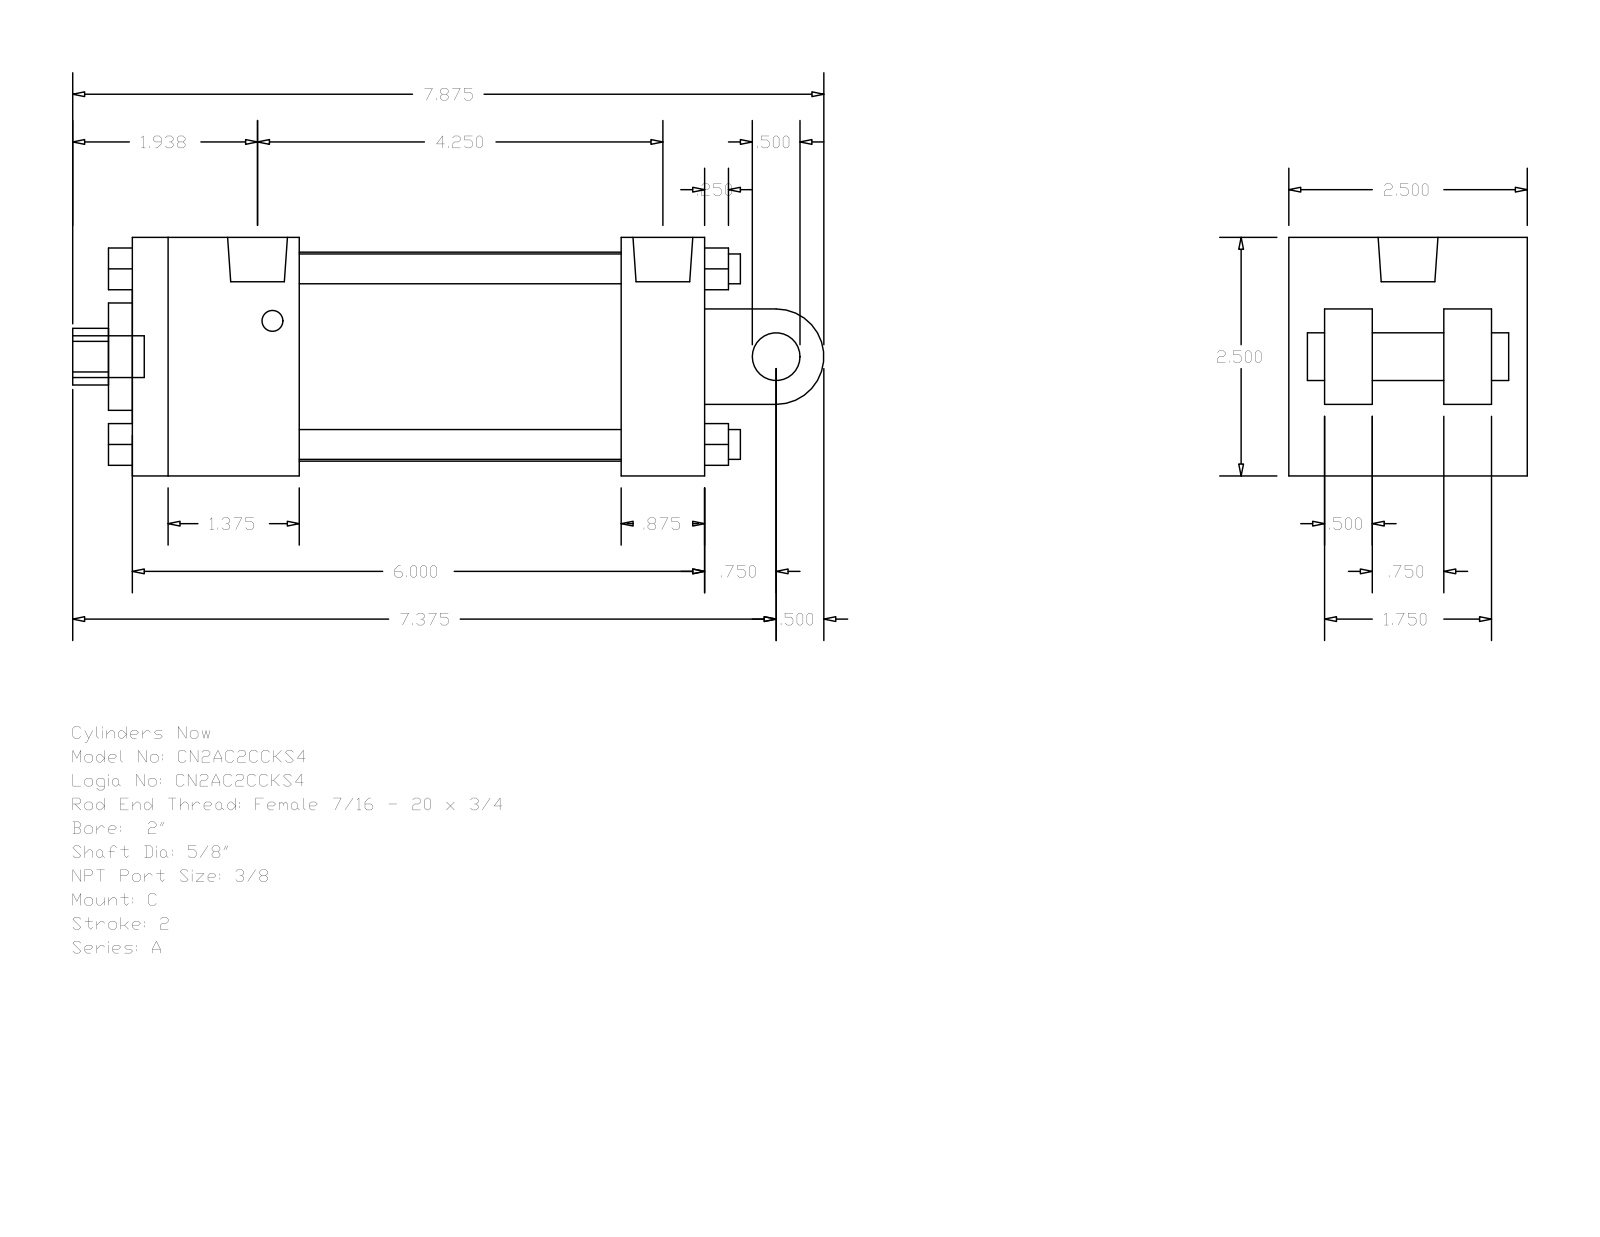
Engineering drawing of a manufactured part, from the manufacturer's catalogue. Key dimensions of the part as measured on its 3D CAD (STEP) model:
Part name (STEP PRODUCT): A_C__0200_0.625
STEP written by: GSSL Pune (CONFIG_CONTROL_DESIGN)
Units: millimetres
Bodies: 0 solids, 135 faces (102 planar, 33 cylindrical, 0 other)
Overall size (bounding box): 200.03 × 63.5 × 63.5
Round holes (diameter × count): ⌀5.56 ×2, ⌀15.88 ×1, ⌀15.93 ×1, ⌀28.57 ×1, ⌀55.63 ×1
Round bosses / shafts (diameter × count): ⌀7.94 ×4, ⌀5.56 ×2, ⌀15.93 ×1, ⌀12.7 ×1, ⌀11.11 ×1
Partial cylindrical surfaces — rounded edges, fillets, slot ends (radius × count): R7.54 ×1, R12.7 ×1
Main face-to-face distances: 63.5, 152.4, 44.45, 9.52, 107.95, 130.17, 85.72, 22.23, 12.7, 41.28
Hole centre spacings: 3.97
